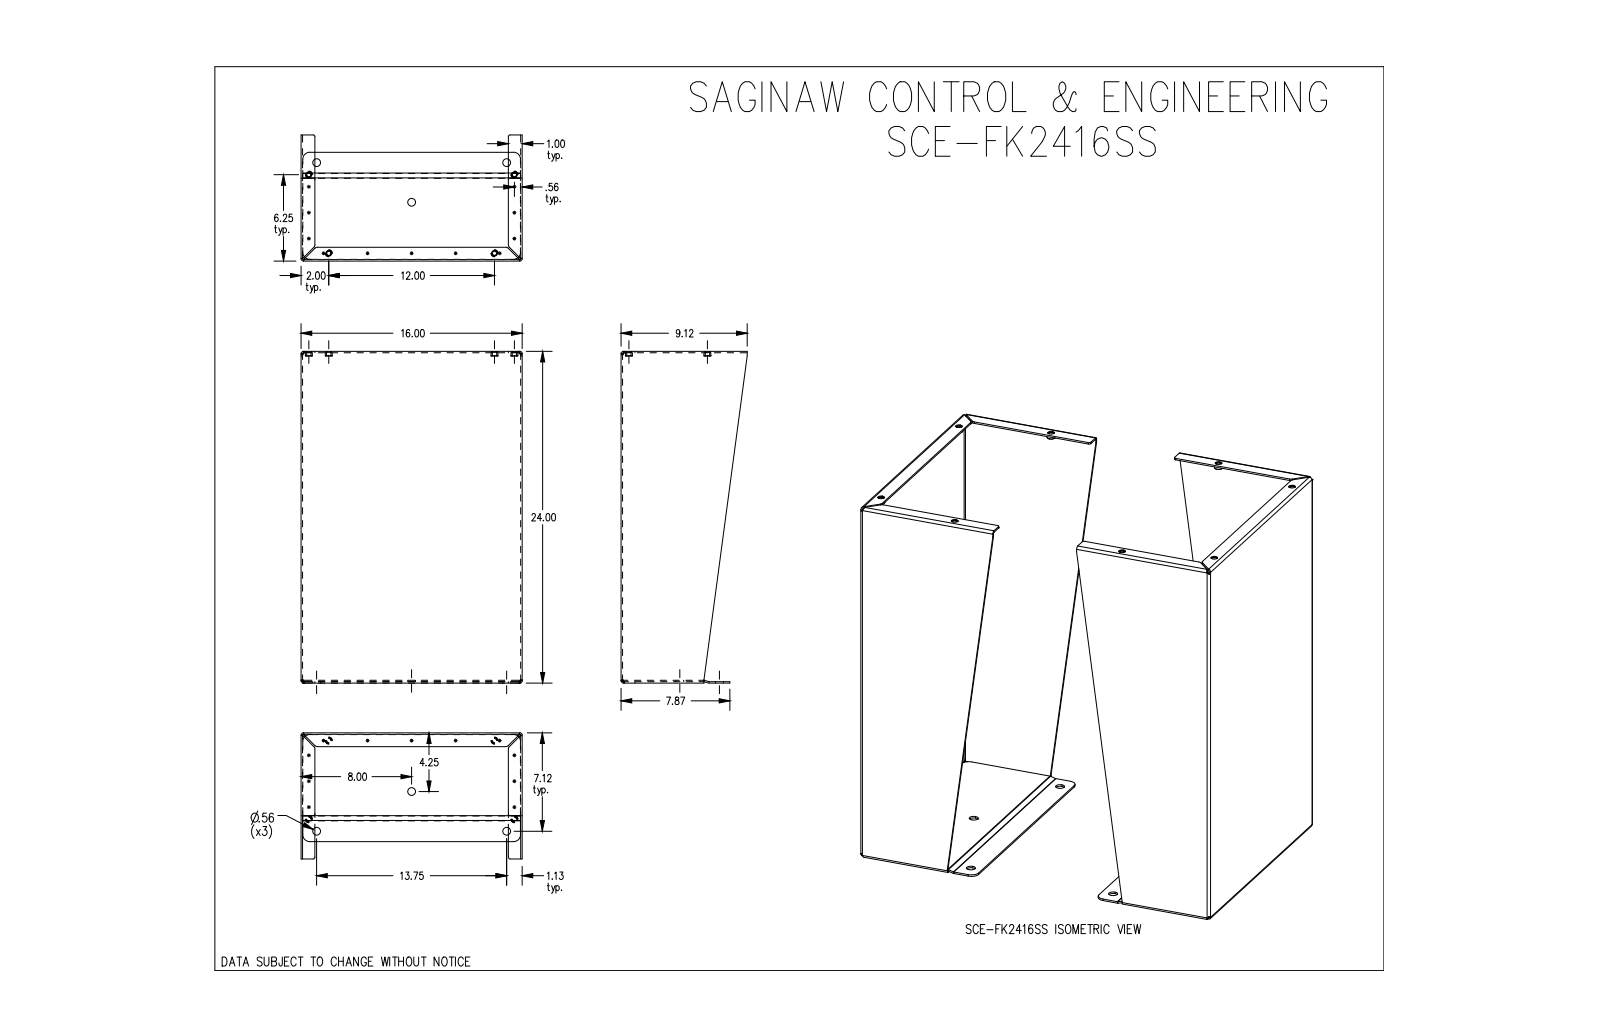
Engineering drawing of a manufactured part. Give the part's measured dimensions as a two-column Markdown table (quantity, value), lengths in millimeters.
| quantity | value |
| --- | --- |
| part name | SCE-FK2416SS |
| STEP written by | SolidWorks 2019 (CONFIG_CONTROL_DESIGN) |
| units | millimeters |
| bodies | 12 solids, 286 faces (120 planar, 110 cylindrical, 56 other) |
| overall size | 609.6 × 609.6 × 406.4 |
| volume | 3 100 000 mm³ |
| surface area | 2 373 000 mm² |
| round holes (diameter × count) | 7.9 × 8, 10.5 × 8, 14.3 × 6 |
| round bosses / shafts (diameter × count) | 12.7 × 8, 10.5 × 8 |
| partial cylindrical surfaces (radius × count) | 4.2 × 16, 1.6 × 14, 3.2 × 8, 5.6 × 8, 12.7 × 8, 1.6 × 2 |
| main face-to-face distances | 2.6, 607, 403.8, 604.3, 609.6, 406.4, 401.1, 2.6, 606.9, 601.7 |
| hole center spacings | 26.3, 149, 168, 178.9, 189.2, 195.6, 270.4, 365.3 |
